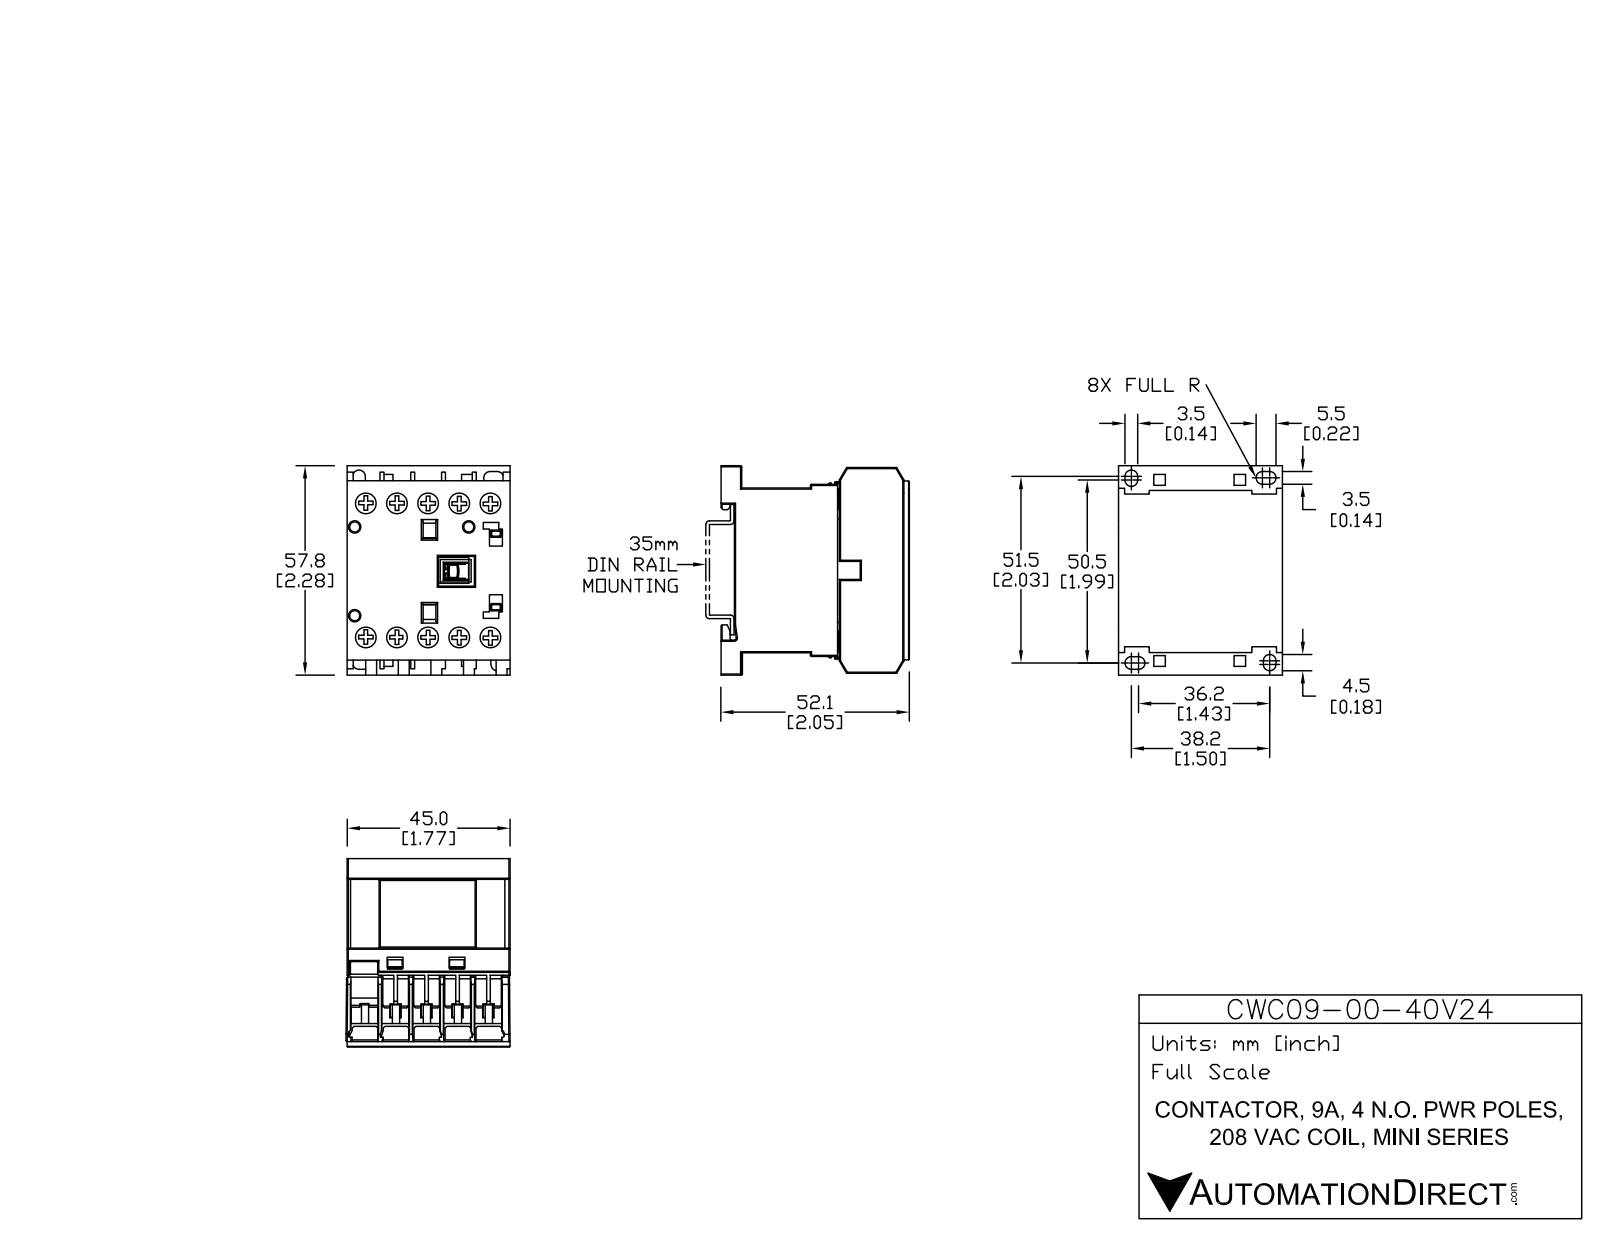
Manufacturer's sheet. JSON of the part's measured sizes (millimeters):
{"part_name": "CWC09-00-40V24", "step_written_by": "SolidWorks 2013 (AUTOMOTIVE_DESIGN)", "units": "millimeters", "bodies": {"solids": 15, "faces": 535, "planar": 445, "cylindrical": 90, "other": 0}, "overall_size": [58.04, 52.12, 45.75], "volume_mm3": 97133, "surface_area_mm2": 30437, "round_holes": [[6.2, 10], [2.8, 3]], "round_bosses_or_shafts": [[5.9, 10]], "partial_cylinders_radius": [[0.3, 20], [1.72, 6], [1.73, 2], [0.32, 1], [0.42, 1], [0.55, 1]], "face_to_face_distances": [8.25, 45.5, 1.25, 16.5, 9.5, 5.5, 17.75, 5.13, 10.63, 7], "hole_center_spacings": [8.55, 37.94, 17.1, 40.72, 36.96, 25.65, 44.99, 6.91]}
